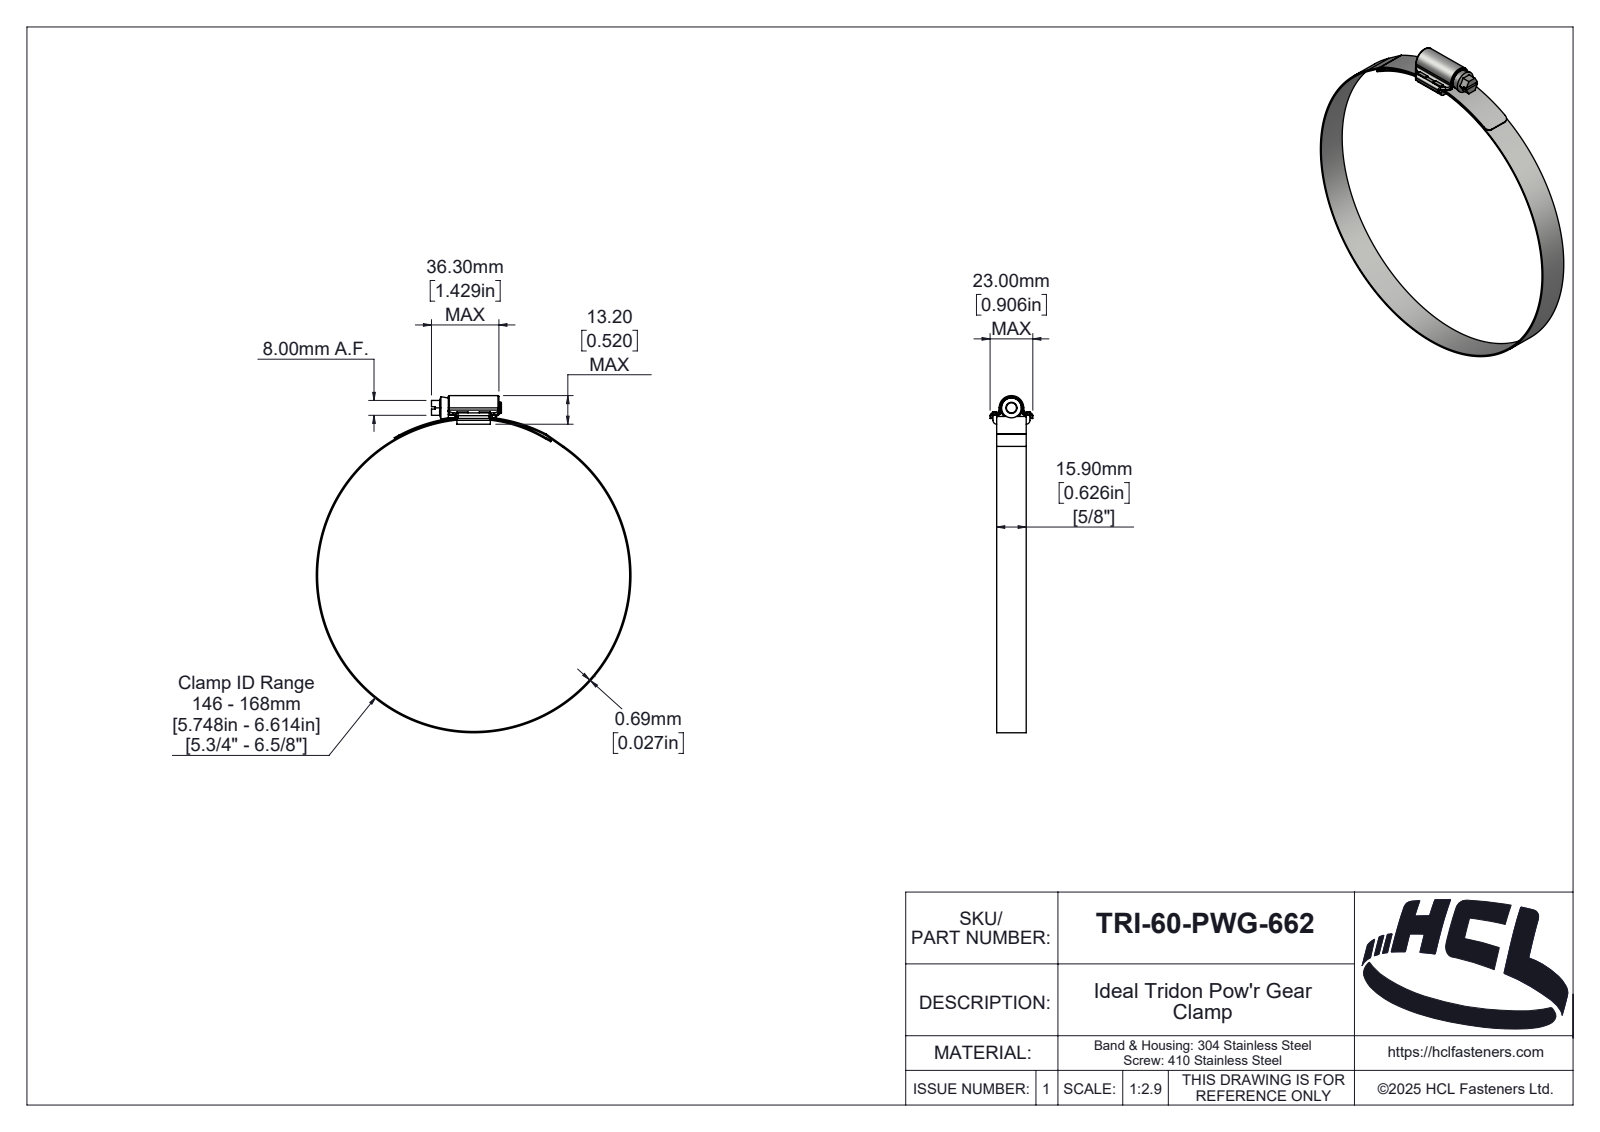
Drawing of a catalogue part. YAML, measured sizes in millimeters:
part_name: "TRI-60-PWG-662"
step_written_by: "SolidWorks 2025 (AUTOMOTIVE_DESIGN)"
units: millimeters
bodies: {solids: 4, faces: 268, planar: 87, cylindrical: 102, other: 79}
overall_size: [181.39, 169.38, 23]
volume: 11982
surface_area: 25137
round_holes:
  - {diameter: 168, count: 1}
round_bosses_or_shafts:
  - {diameter: 169.38, count: 1}
  - {diameter: 10.7, count: 1}
  - {diameter: 6, count: 1}
partial_cylinders:
  - {radius: 1, count: 14}
  - {radius: 0.5, count: 4}
  - {radius: 1.5, count: 4}
  - {radius: 2, count: 3}
  - {radius: 0.1, count: 2}
  - {radius: 2.1, count: 2}
  - {radius: 3, count: 2}
  - {radius: 0.46, count: 1}
face_to_face_distances: [15.9, 2, 0.69, 17.9, 4.9, 1.2, 4.55, 3.35, 15.35, 2.55]
